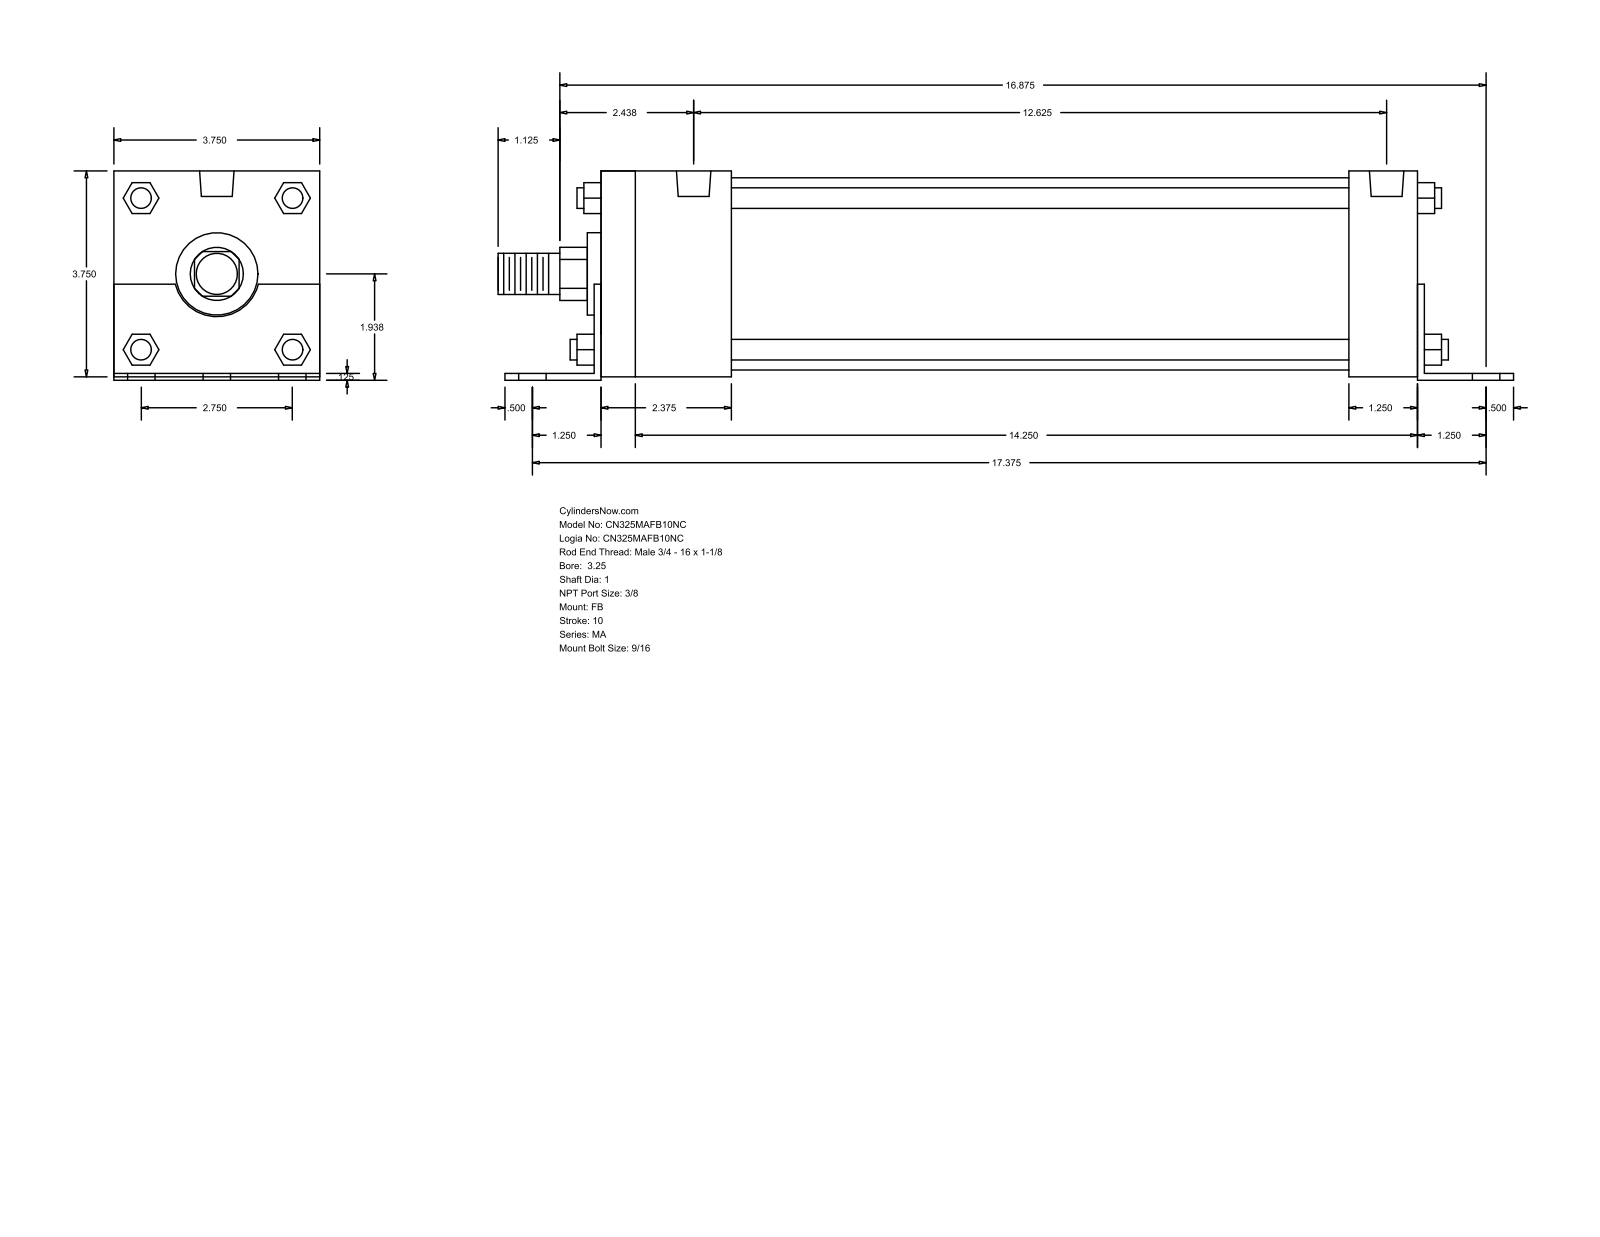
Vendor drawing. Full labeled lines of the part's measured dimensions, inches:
Part name (STEP PRODUCT): MA_FB__0325_1
STEP written by: GSSL Pune (CONFIG_CONTROL_DESIGN)
Units: inches
Bodies: 0 solids, 140 faces (105 planar, 35 cylindrical, 0 other)
Overall size (bounding box): 18.5 × 3.813 × 3.75
Round holes (diameter × count): ⌀0.563 ×6, ⌀0.437 ×4, ⌀0.627 ×2
Round bosses / shafts (diameter × count): ⌀0.375 ×4, ⌀3.5 ×1, ⌀1.5 ×1, ⌀1 ×1, ⌀0.75 ×1
Partial cylindrical surfaces — rounded edges, fillets, slot ends (radius × count): R0.484 ×1, R0.78 ×1
Main face-to-face distances: 3.75, 0.125, 0.063, 3.812, 0.062, 3.687, 15, 14.875, 15.125, 1.375
Hole centre spacings: 1.375, 17.429, 17.375, 2.275, 2.427, 2.75, 3.243, 3.414
